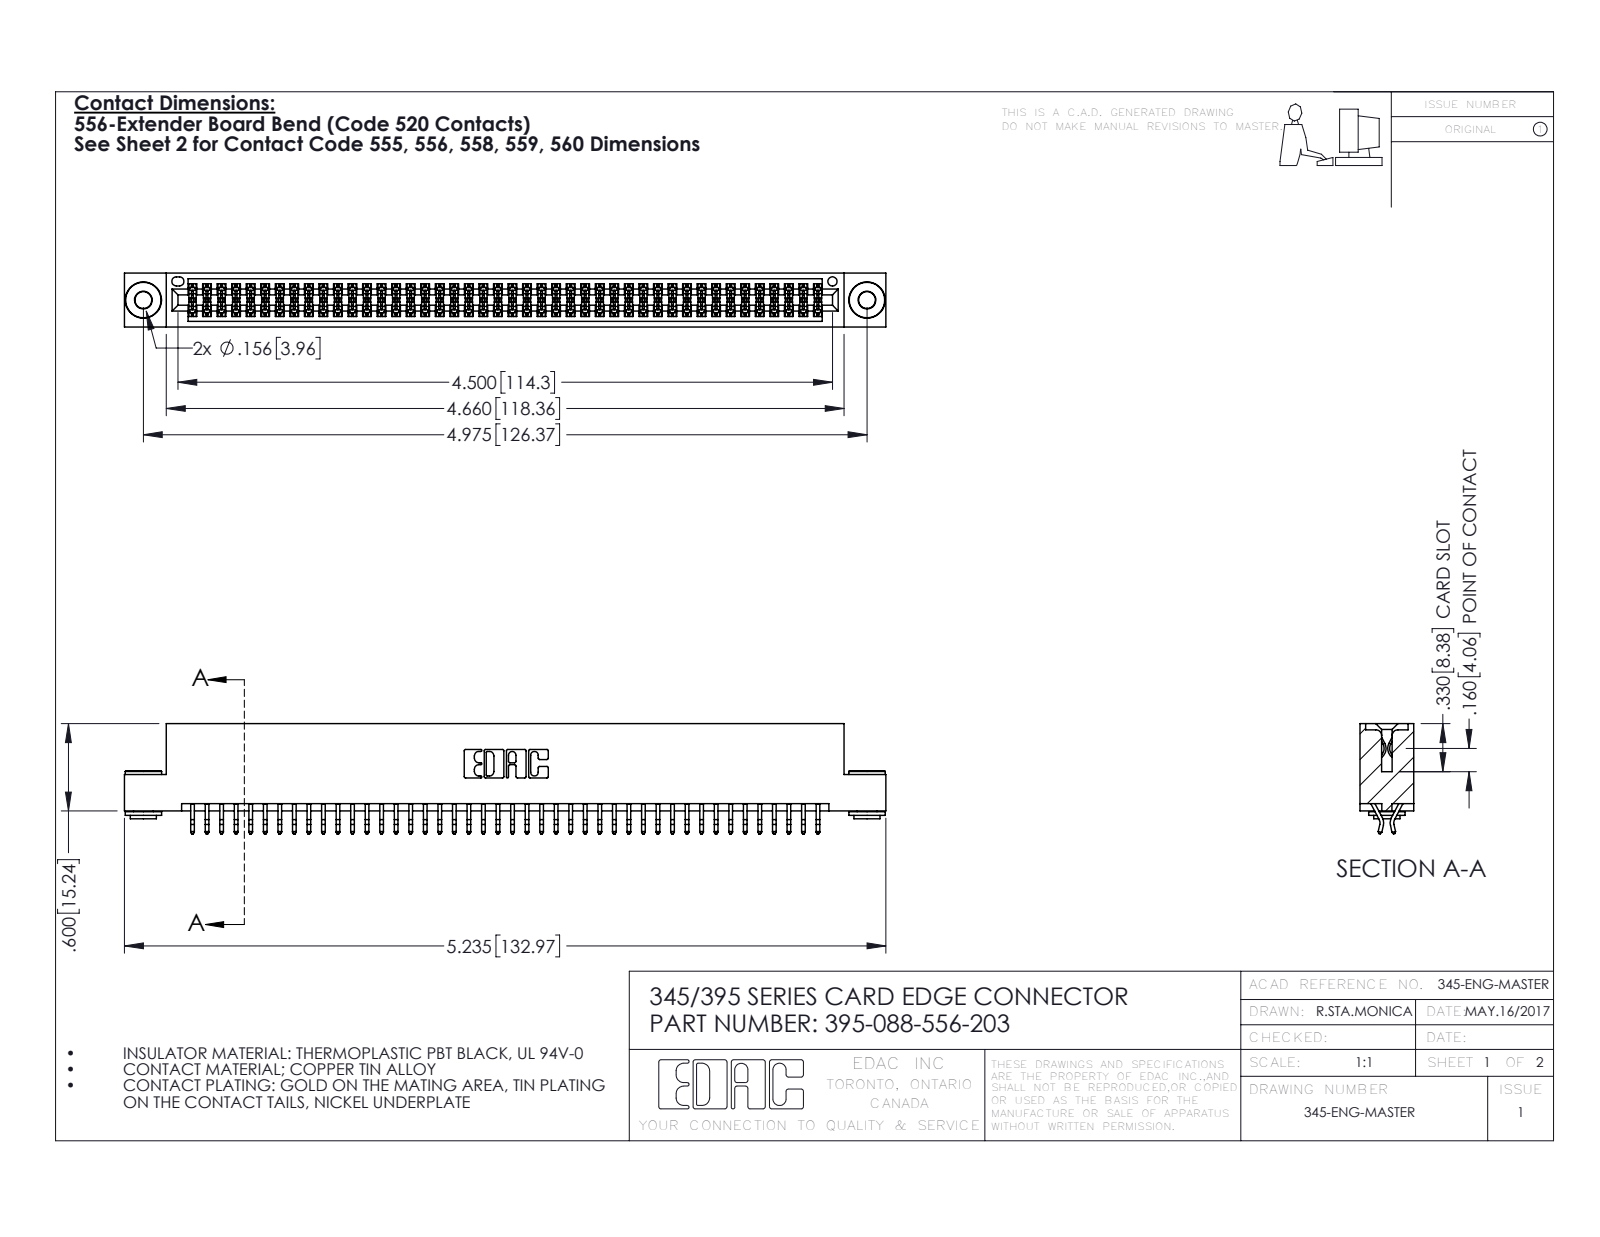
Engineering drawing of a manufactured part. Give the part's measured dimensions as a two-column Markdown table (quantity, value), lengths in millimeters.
| quantity | value |
| --- | --- |
| part name | 345-292-001_556 Tail; 345-250-002_345-250-002-102; 395-088-556-203; 345 Part_Flush Mounting Lugs - 0.156 Dia-TH |
| STEP written by | SolidWorks 2016 (CONFIG_CONTROL_DESIGN) |
| units | millimeters |
| bodies | 91 solids, 5092 faces (3346 planar, 1738 cylindrical, 8 other) |
| overall size | 133 × 19.2 × 9.4 |
| volume | 12 900 mm³ |
| surface area | 19 310 mm² |
| round holes (diameter × count) | 2.9 × 2, 4 × 2, 1.6 × 1 |
| round bosses / shafts (diameter × count) | 6.4 × 2, 4.6 × 2, 3.5 × 2 |
| partial cylindrical surfaces (radius × count) | 0.2 × 132, 0.3 × 22, 0.2 × 6, 0.8 × 6, 0.7 × 3, 0.3 × 2, 0.4 × 2, 0.5 × 2 |
| main face-to-face distances | 1.8, 7.6, 5.1, 9.4, 0.6, 2.5, 6.9, 5.7, 4.4, 3.8 |
| hole center spacings | 6.9, 120.4, 126.4 |
